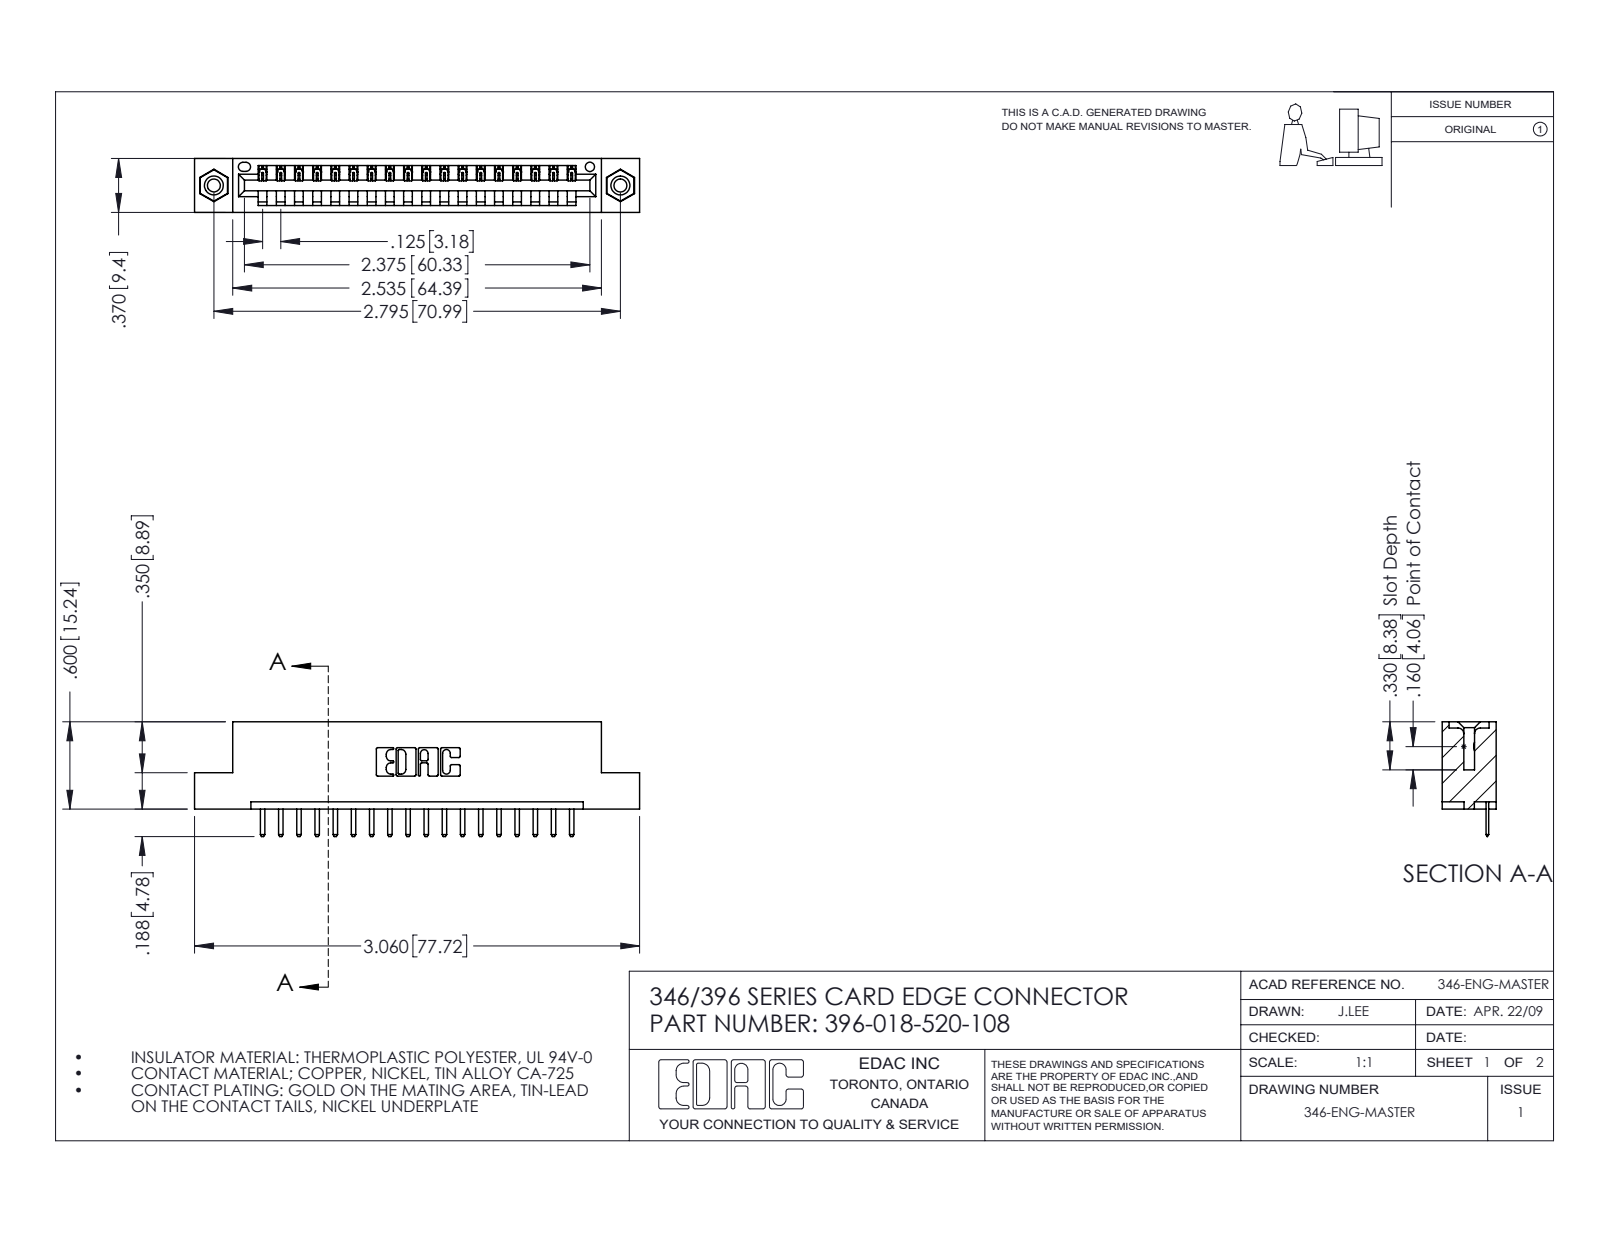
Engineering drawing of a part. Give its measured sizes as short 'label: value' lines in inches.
name: 345-250-001_345-250-003-102; 345-292-001_345-293-120; 396-018-520-108; 346 Part_Flush Mounting Lugs - 0.156 Dia-TI
written by: SolidWorks 2016 (CONFIG_CONTROL_DESIGN)
unit: in
bodies: 21 solids, 1298 faces (864 planar, 418 cylindrical, 16 other)
size: 3.06 × 0.788 × 0.37
volume: 0.44 in³; area: 13.34 in²
holes: 2× ⌀0.089, 2× ⌀0.125, 2× ⌀0.156, 1× ⌀0.064
bosses: 2× ⌀0.155
rounds: 38× R0.01, 36× R0.006, 22× R0.01, 6× R0.007, 6× R0.031, 3× R0.026, 2× R0.031, 2× R0.04
face distances: 0.048, 0.322, 0.37, 0.25, 0.148, 0.222, 0.1, 0.174, 0.072, 0.298
hole spacings: 0.246, 2.588, 2.795
